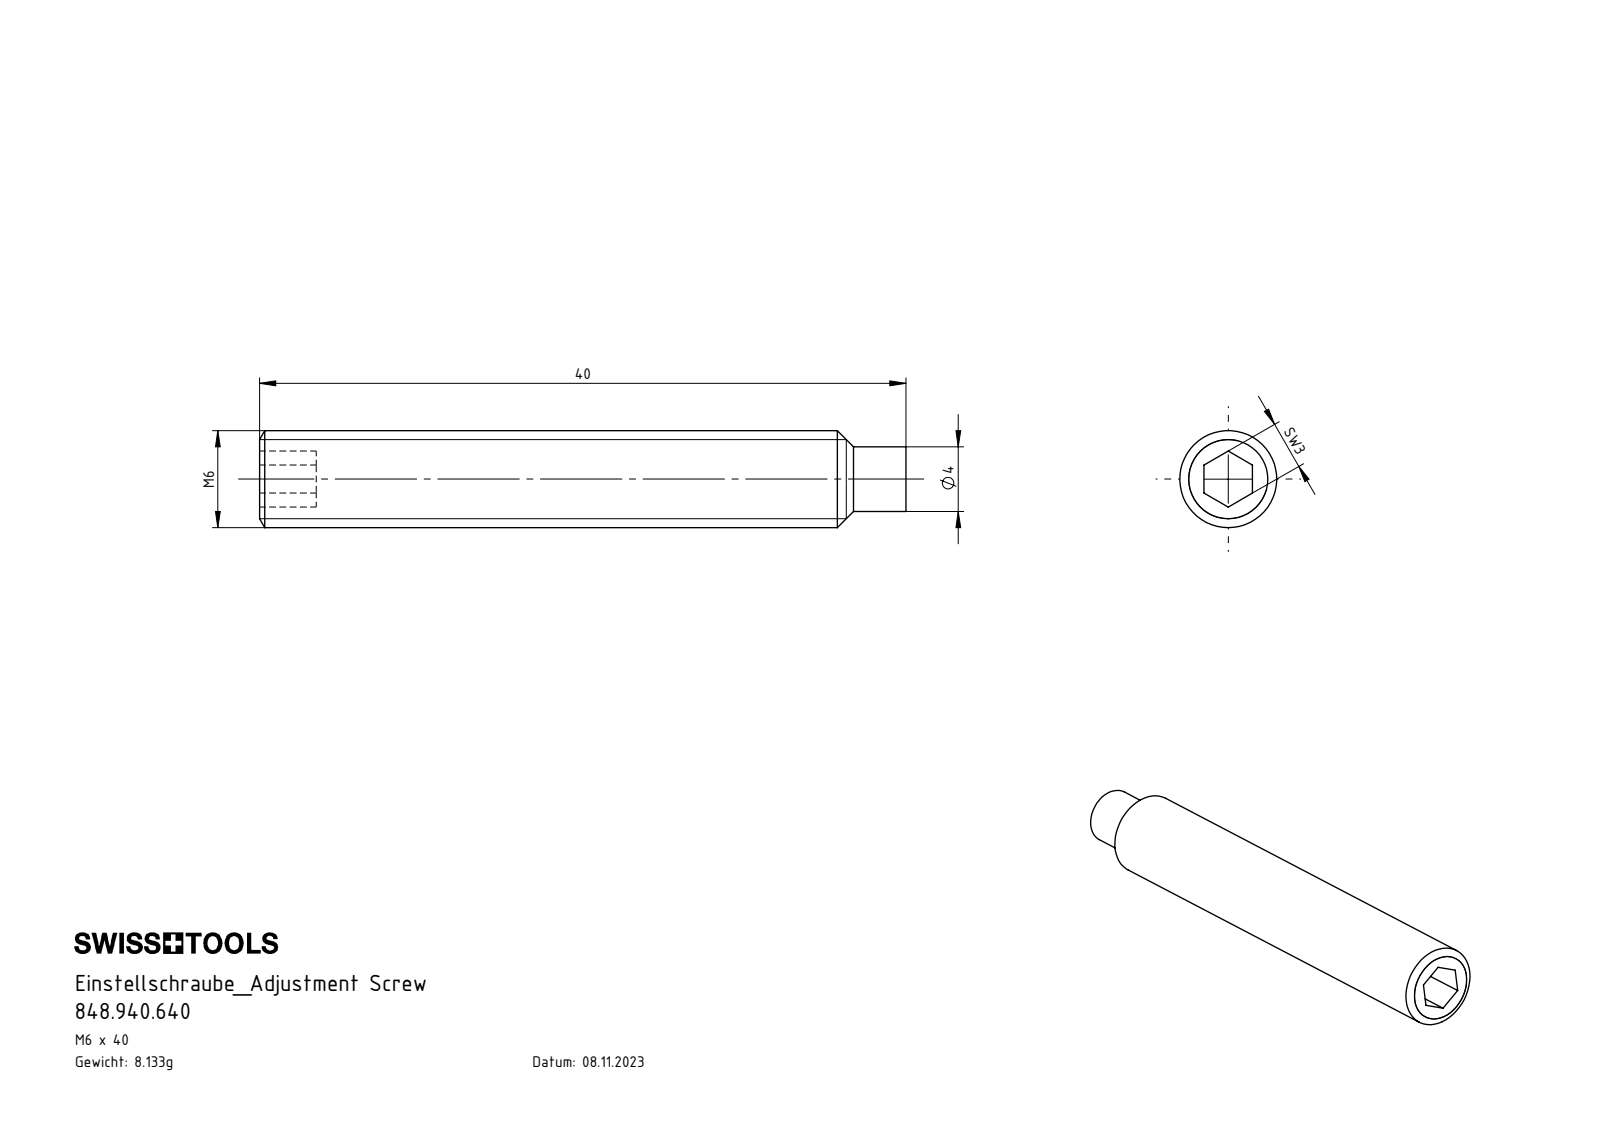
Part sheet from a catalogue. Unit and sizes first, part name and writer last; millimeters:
Units: millimetres
Overall size (bounding box): 40 × 6 × 6
Round bosses / shafts (diameter × count): ⌀6 ×1, ⌀4 ×1
Main face-to-face distances: 3, 40, 3.5, 36.5
Volume: 1 043 mm³ · Surface area: 810 mm²
Bodies: 1 solid, 17 faces (9 planar, 4 cylindrical, 4 other)
Part name (STEP PRODUCT): 848.940.640
STEP written by: SolidWorks 2022 (AUTOMOTIVE_DESIGN)
